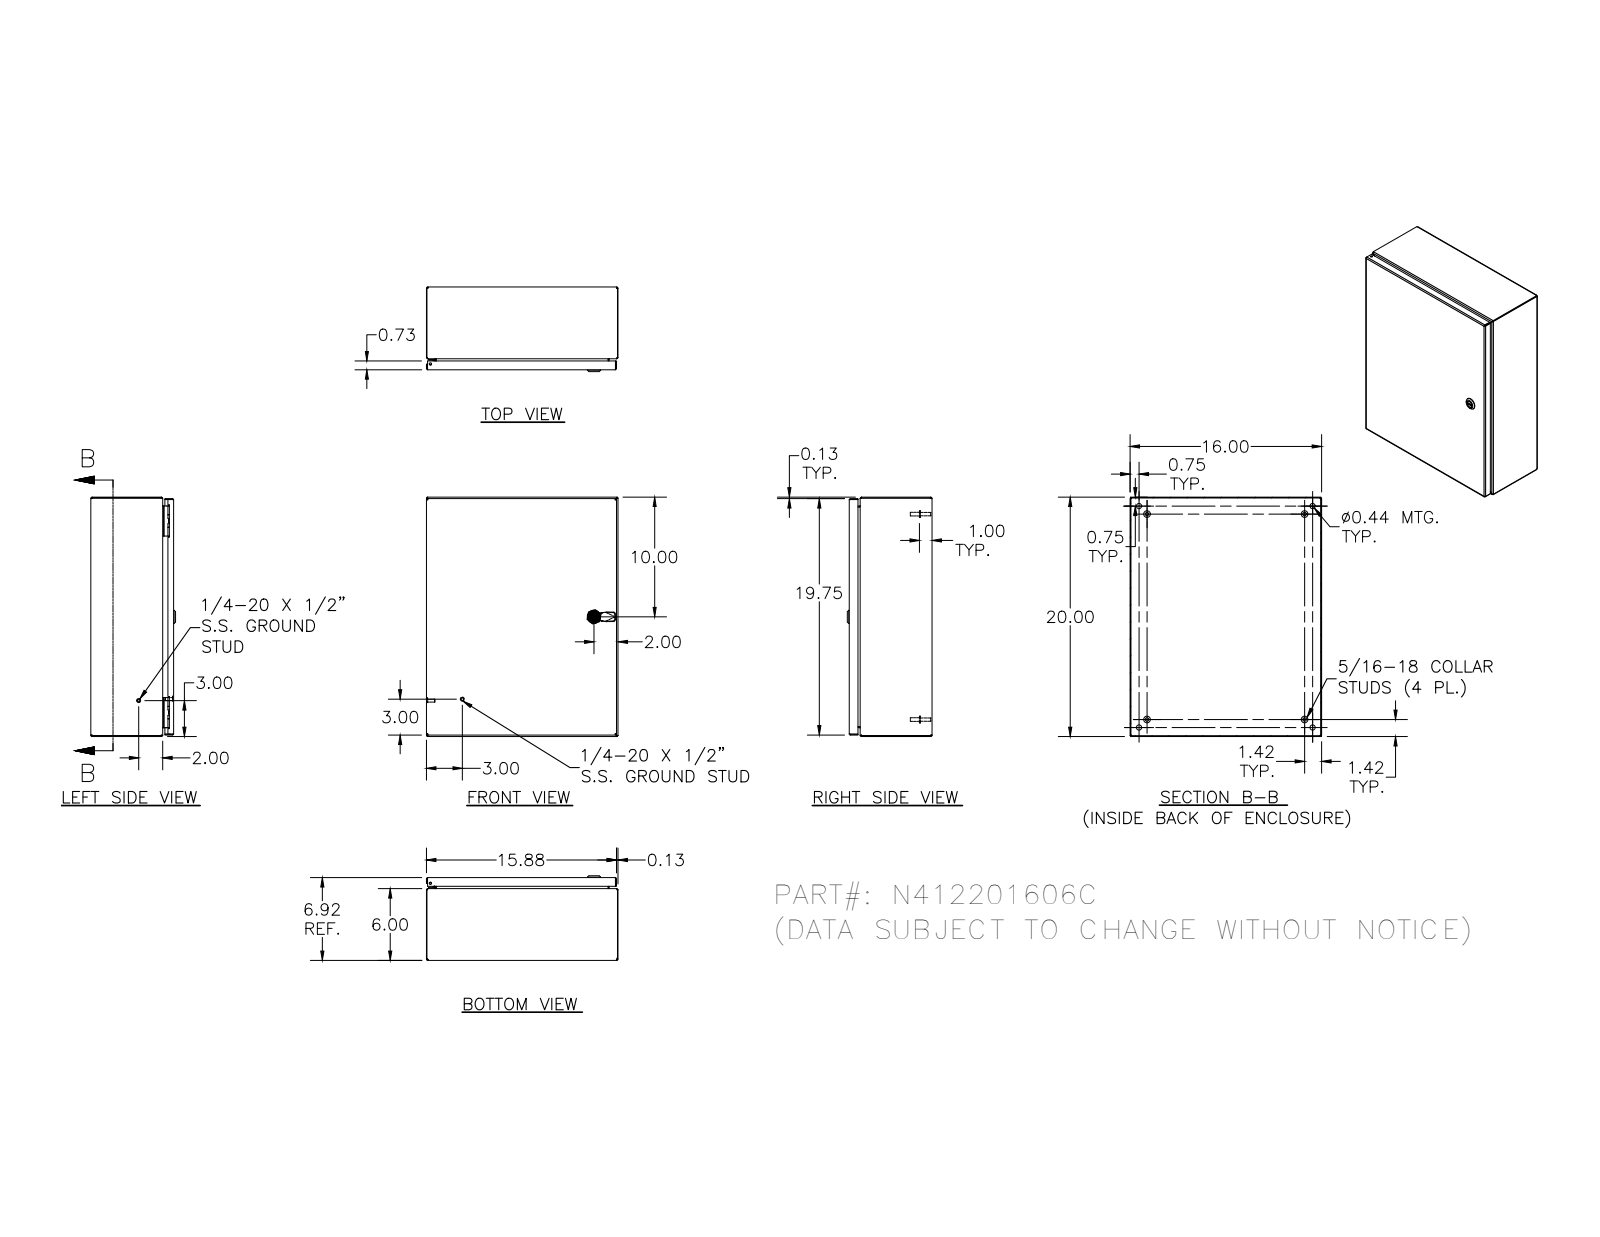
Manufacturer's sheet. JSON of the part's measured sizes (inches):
{"part_name": "N412201606C", "step_written_by": "SolidWorks 2018 (AUTOMOTIVE_DESIGN)", "units": "inches", "bodies": {"solids": 33, "faces": 1449, "planar": 530, "cylindrical": 547, "other": 372}, "overall_size": [20, 16, 7.075], "volume_in3": 90.39, "surface_area_in2": 2460, "round_holes": [[0.188, 5], [0.093, 4], [0.152, 4], [0.167, 4], [0.172, 4], [0.437, 4], [0.156, 2], [0.187, 1], [0.197, 1], [0.315, 1], [0.394, 1], [0.402, 1]], "round_bosses_or_shafts": [[0.25, 10], [0.131, 5], [0.563, 4], [0.36, 4], [0.32, 4], [0.3, 4], [0.275, 4], [0.256, 4]], "partial_cylinders_radius": [[0.012, 30], [0.031, 30], [0.05, 26], [0.105, 20], [0.016, 18], [0.125, 16], [0.02, 13], [0.032, 8]], "face_to_face_distances": [0.074, 6.843, 6.769, 6.917, 0.074, 15.926, 16, 15.852, 15.926, 20], "hole_center_spacings": [16, 0.66, 0.656, 1.307, 1.965, 15.34, 16.66, 15.614]}
